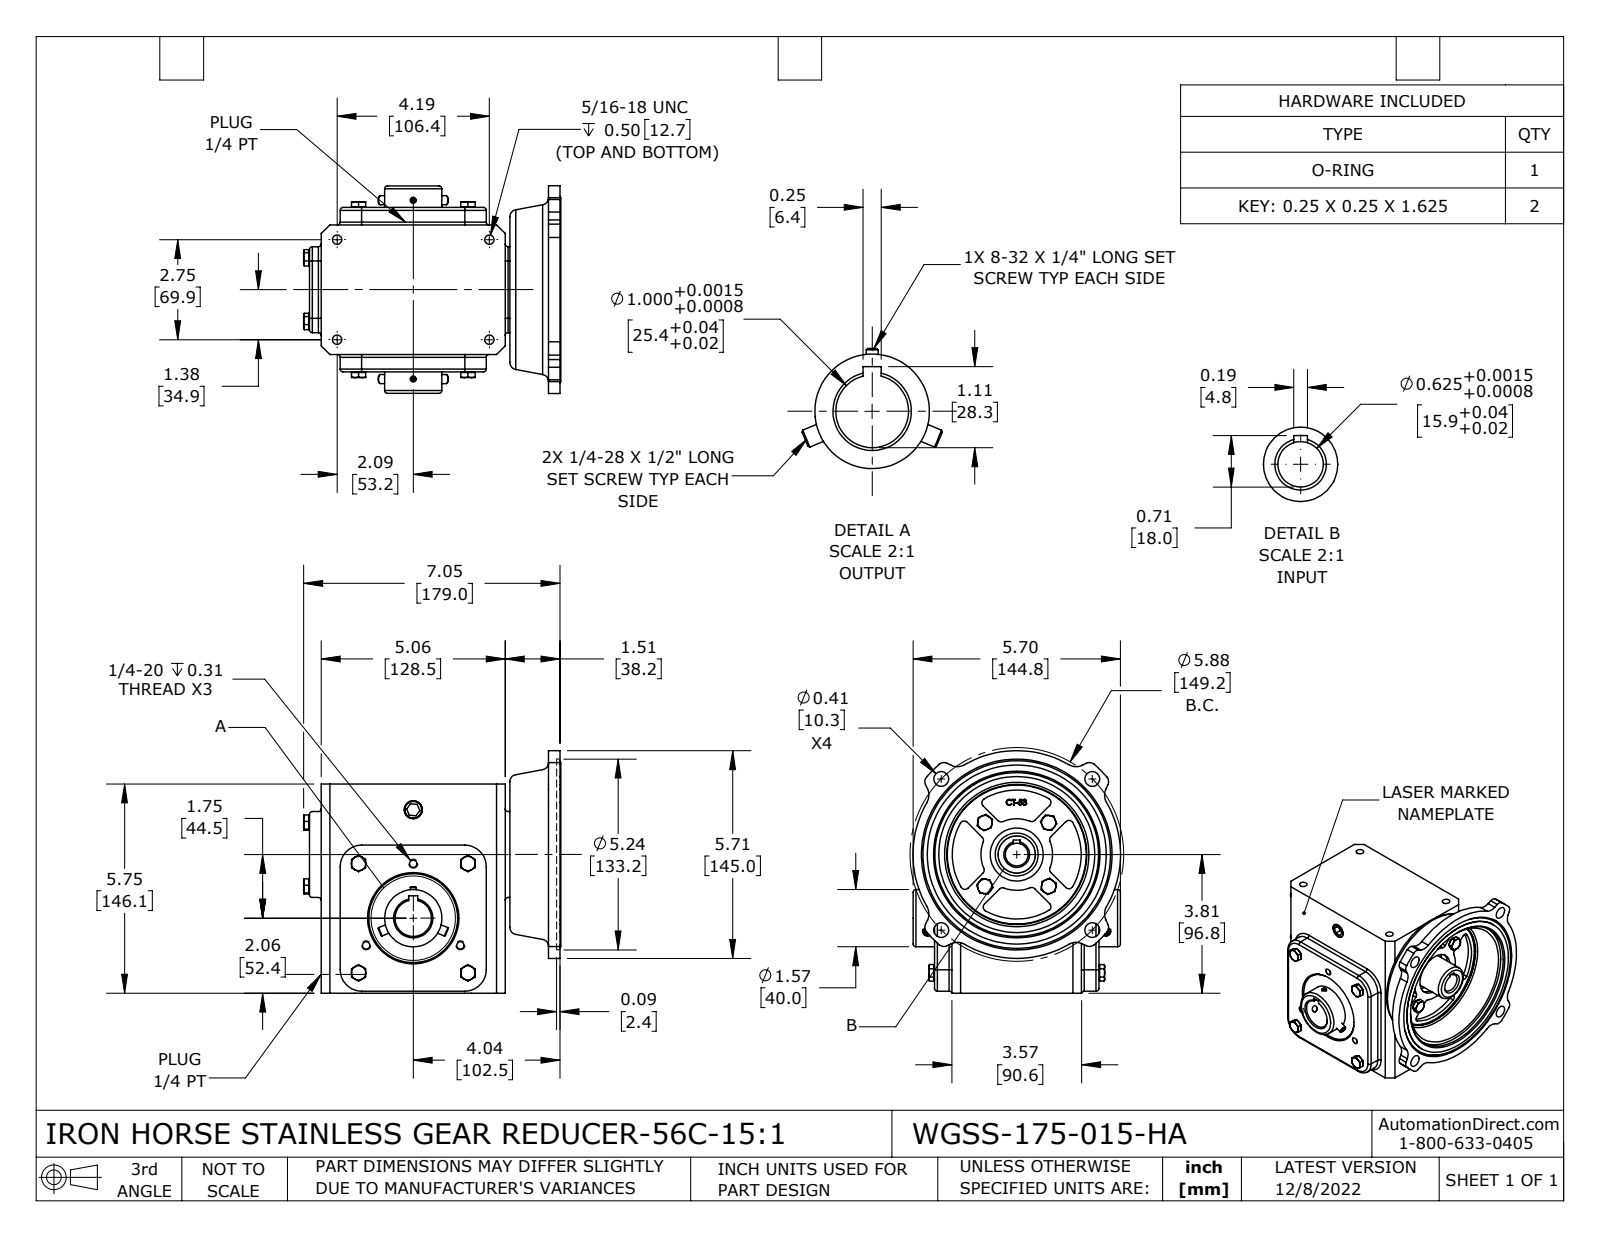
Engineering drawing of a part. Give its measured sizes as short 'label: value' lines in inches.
name: WGSS-175-015-HA
written by: SolidWorks 2021 (CONFIG_CONTROL_DESIGN)
unit: in
bodies: 7 solids, 891 faces (390 planar, 231 cylindrical, 270 other)
size: 7.071 × 6.691 × 5.709
volume: 127 in³; area: 281 in²
holes: 4× ⌀0.213, 4× ⌀0.257, 4× ⌀0.406, 3× ⌀0.201, 2× ⌀0.136, 1× ⌀0.625, 1× ⌀0.866, 1× ⌀1, 1× ⌀1.102, 1× ⌀1.457, 1× ⌀1.575, 1× ⌀3.819
bosses: 8× ⌀0.394, 4× ⌀0.25, 2× ⌀0.164, 1× ⌀4.921, 1× ⌀2.441, 1× ⌀1.575, 1× ⌀1.181
rounds: 28× R0.079, 16× R0.118, 12× R0.394, 8× R0.197, 4× R0.591, 1× R0.984, 1× R1.772, 1× R2.854
face distances: 0.48, 4.04, 5.75, 5.06, 0.157, 3.56, 4.52, 0.315, 6.565, 1.506
hole spacings: 2.357, 2.937, 4.154, 1.496, 2.591, 4.913, 2.75, 4.188
